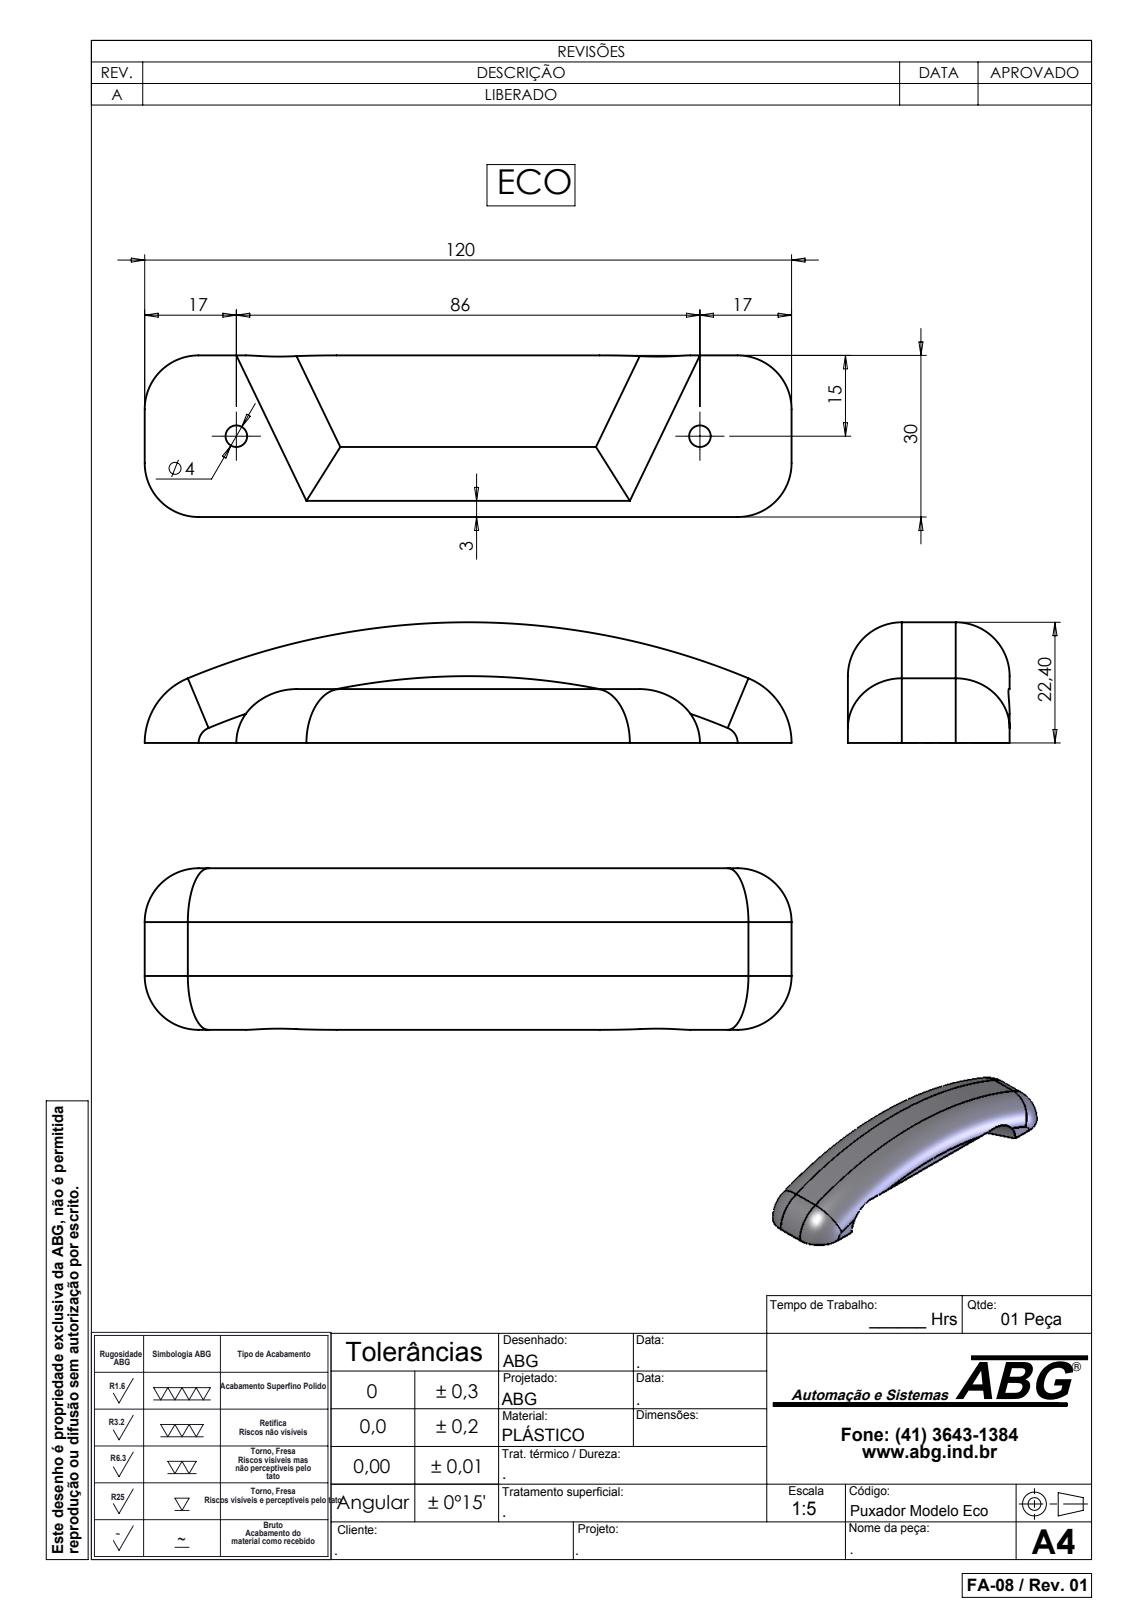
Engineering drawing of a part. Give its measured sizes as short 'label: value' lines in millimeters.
name: Puxador Modelo Eco
written by: SolidWorks 2007 (CONFIG_CONTROL_DESIGN)
unit: mm
bodies: 1 solid, 24 faces (8 planar, 10 cylindrical, 6 other)
size: 120 × 30 × 22.4
volume: 40 261 mm³; area: 10 733 mm²
holes: 2× ⌀4
rounds: 3× R10, 2× R13, 1× R135.2
face distances: 10, 30
hole spacings: 86
